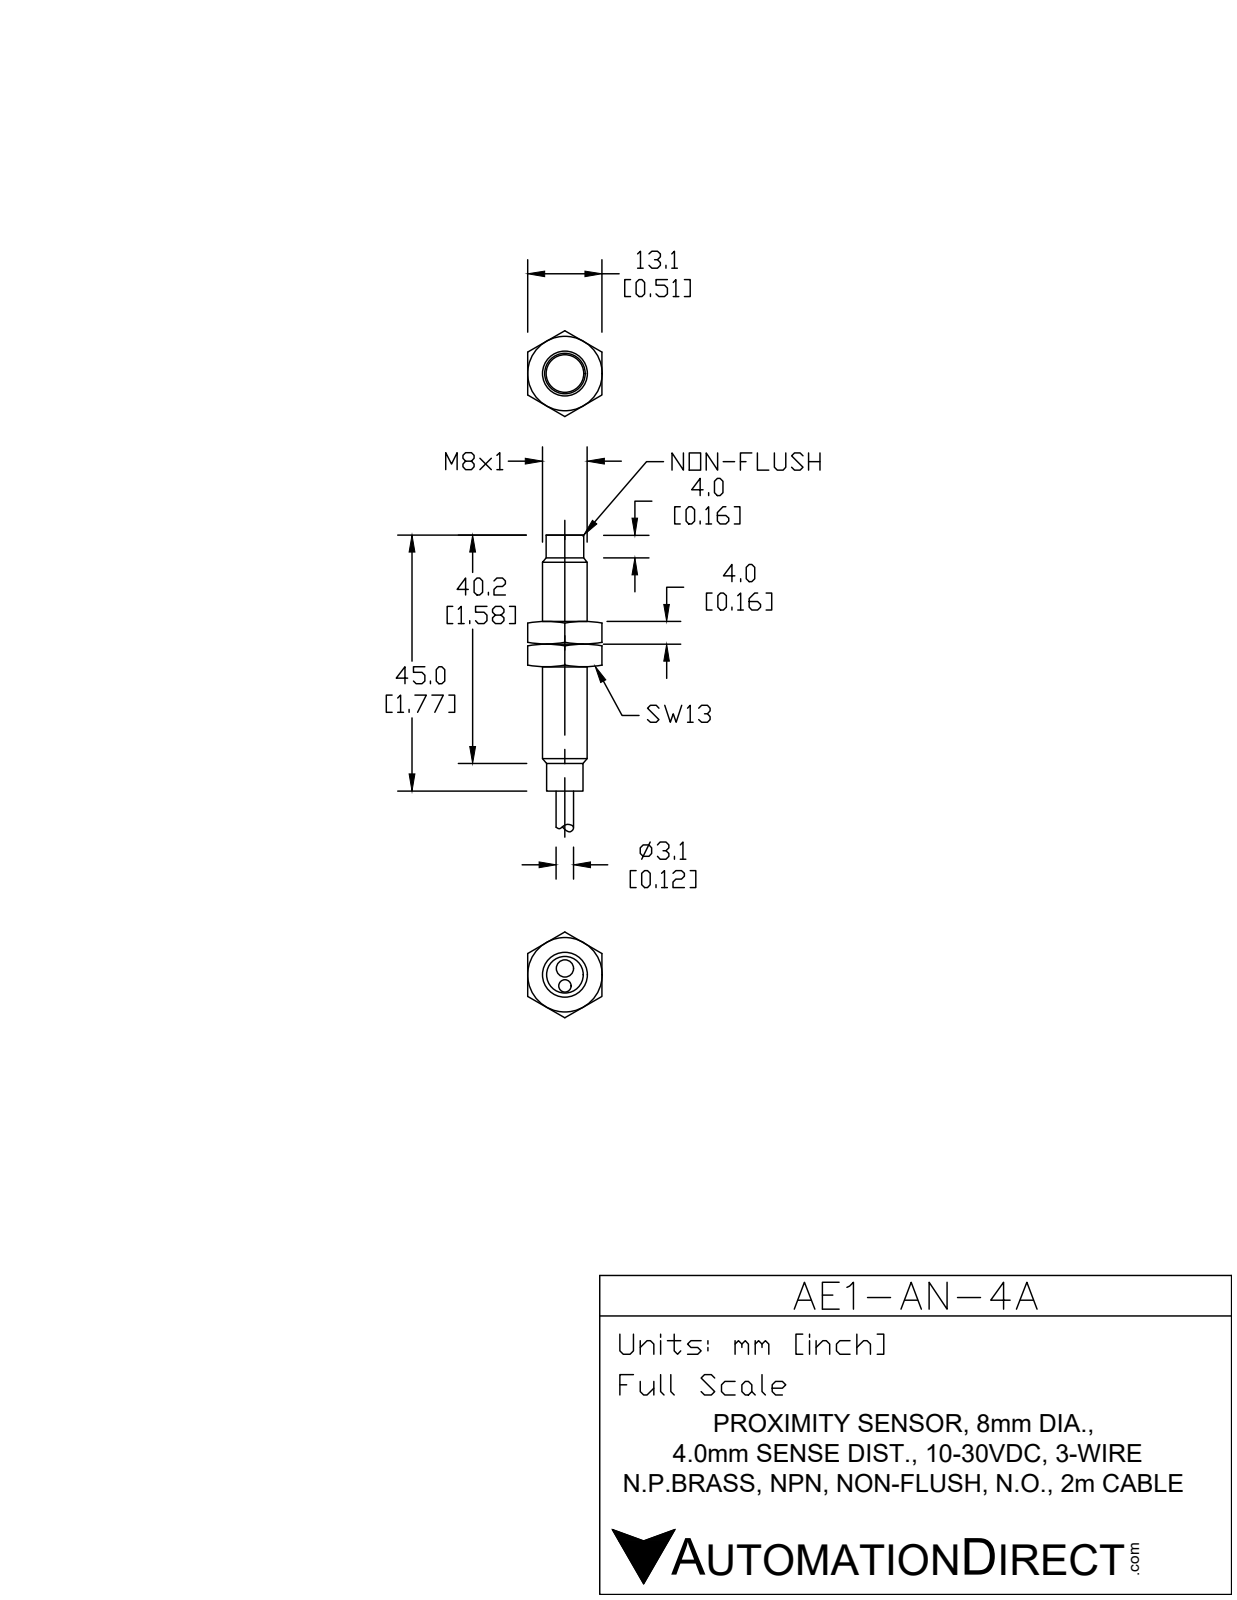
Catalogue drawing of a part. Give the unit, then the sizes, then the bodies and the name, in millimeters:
Units: millimetres
Overall size (bounding box): 82.6 × 8 × 8
Round holes (diameter × count): ⌀3.1 ×1, ⌀5.8 ×1
Round bosses / shafts (diameter × count): ⌀8 ×1, ⌀6.5 ×1, ⌀6.5 ×1
Main face-to-face distances: 36.2, 4, 40.2, 44.5, 40.5, 4.3, 2.4, 42.6, 38.6, 1.9
Hole centre spacings: 1.1
Volume: 2 380 mm³ · Surface area: 1 726 mm²
Bodies: 4 solids, 30 faces (10 planar, 12 cylindrical, 8 other)
Part name (STEP PRODUCT): AE1-AN-4A
STEP written by: SolidWorks 2017 (AUTOMOTIVE_DESIGN)
